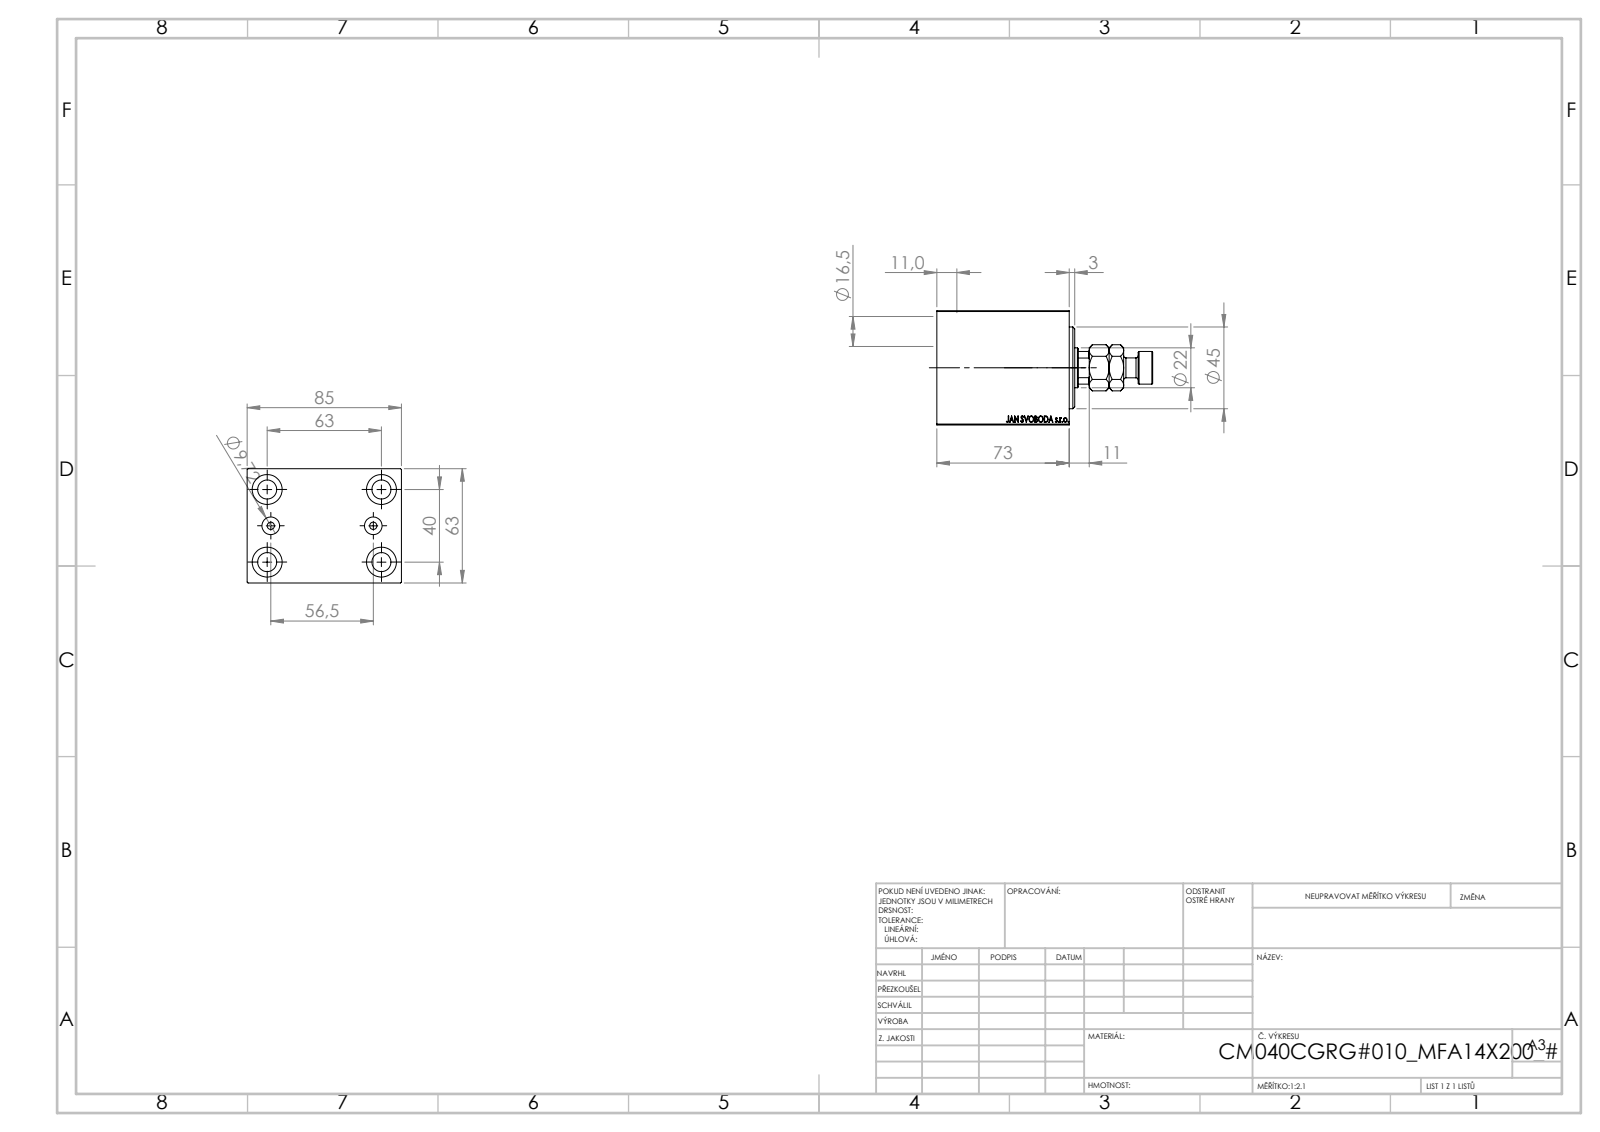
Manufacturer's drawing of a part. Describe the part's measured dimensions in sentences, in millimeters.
The part is named "V450CM_C_VCP; V450CM_C_Body; V450CM_VC_B; MFA". Its 3-D file was written by "SolidWorks 2019 (CONFIG_CONTROL_DESIGN)". It is 4 solids with 910 faces: 424 planar, 60 cylindrical and 426 other. Overall it measures 119 by 85 by 63 millimeters. Its volume is 357 869 cubic millimeters and its surface area 70 763 square millimeters. Round holes: 4 of diameter 10.5, 4 of diameter 16.5, 2 of diameter 4, 2 of diameter 9.72, 1 of diameter 12.5, 1 of diameter 22, 1 of diameter 25.5, 1 of diameter 40, 1 of diameter 42, 1 of diameter 45. Round bosses or shafts: 1 of diameter 18, 1 of diameter 11. Partial cylindrical surfaces (rounded edges, fillets, slot ends): 1 of radius 10.5. The main face-to-face distances are 63, 85, 22, 73, 51, 11, 62, 8, 21.6, 29.4. The hole center spacings are 37.31, 20.1, 20.5, 40, 61.82, 63, 64.2, 74.63.
